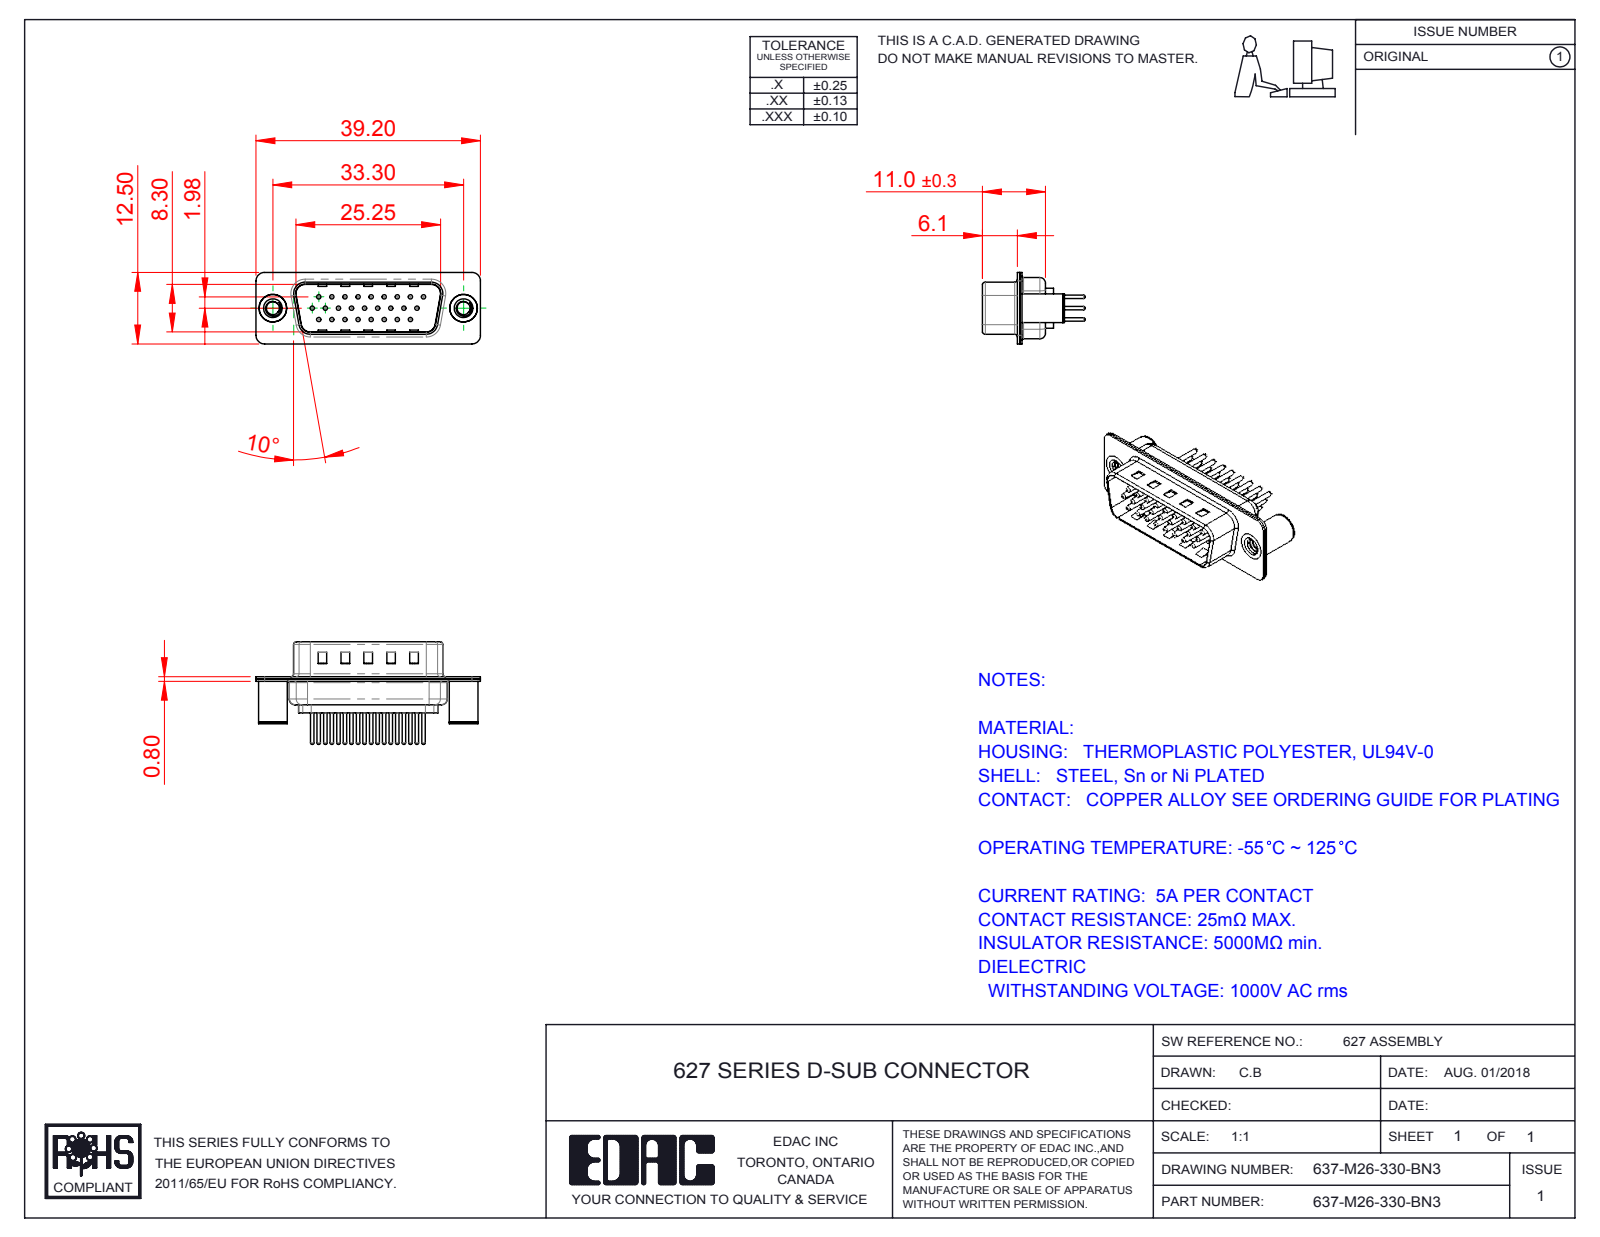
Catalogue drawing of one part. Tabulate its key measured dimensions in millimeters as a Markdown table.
| quantity | value |
| --- | --- |
| part name | 637M Contact Row 3_30; 637M Shell Rear_26 Contacts; 637M 4-40 Threaded Board Spacer; 637M Housing_26 Contacts (+4 more) |
| STEP written by | SolidWorks 2016 (CONFIG_CONTROL_DESIGN) |
| units | millimeters |
| bodies | 31 solids, 1336 faces (321 planar, 521 cylindrical, 494 other) |
| overall size | 39.2 × 17.9 × 12.5 |
| volume | 2 032 mm³ |
| surface area | 6 009 mm² |
| round holes (diameter × count) | 0.75 × 26, 1.6 × 26, 2 × 26, 2.26 × 2, 3.26 × 2, 4 × 2, 4.8 × 2 |
| round bosses / shafts (diameter × count) | 1.5 × 26, 0.6 × 26, 5 × 2, 4.9 × 2 |
| partial cylindrical surfaces (radius × count) | 1.5 × 16, 2 × 12, 0.5 × 8, 1.6 × 8, 0.25 × 4, 0.6 × 4, 0.65 × 4, 0.9 × 4 |
| main face-to-face distances | 0.4, 0.8, 9.5, 9.1, 8.7, 9.9, 6.3, 0.75, 5.5, 0.35 |
| hole center spacings | 3.96, 2.28, 4.57, 6.05, 2.29, 8.24, 6.86, 10.48 |
